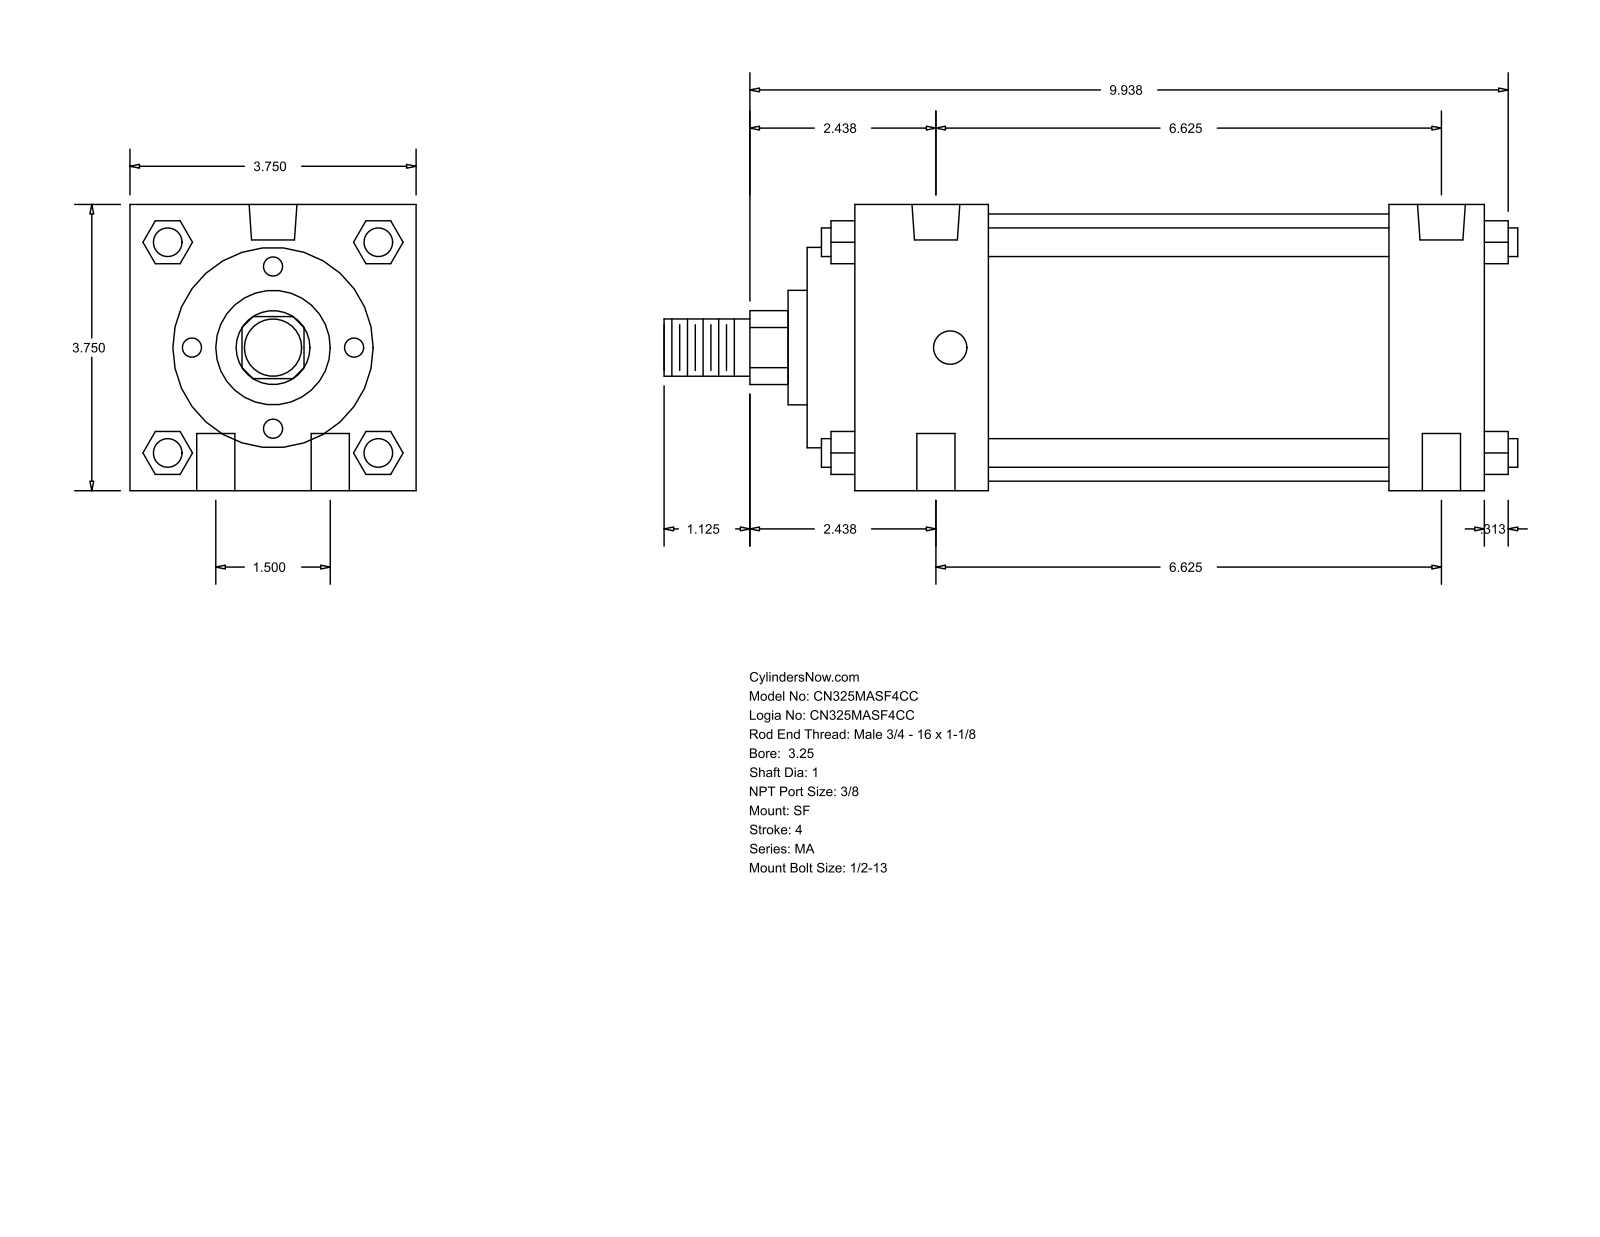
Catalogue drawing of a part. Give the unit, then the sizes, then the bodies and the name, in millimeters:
Units: millimetres
Overall size (bounding box): 284.16 × 95.25 × 95.25
Round holes (diameter × count): ⌀12.7 ×4, ⌀11.11 ×2, ⌀15.93 ×2
Round bosses / shafts (diameter × count): ⌀9.53 ×4, ⌀88.9 ×1, ⌀66.67 ×1, ⌀38.1 ×1, ⌀25.4 ×1, ⌀19.05 ×1
Partial cylindrical surfaces — rounded edges, fillets, slot ends (radius × count): R12.29 ×1
Main face-to-face distances: 95.24, 209.55, 225.42, 177.8, 31.75, 44.46, 133.34, 165.09, 15.87, 60.33
Hole centre spacings: 19.05, 169.35, 168.28, 38.1, 172.54, 158.76
Bodies: 0 solids, 126 faces (95 planar, 31 cylindrical, 0 other)
Part name (STEP PRODUCT): MA_SF__0325_1
STEP written by: GSSL Pune (CONFIG_CONTROL_DESIGN)
